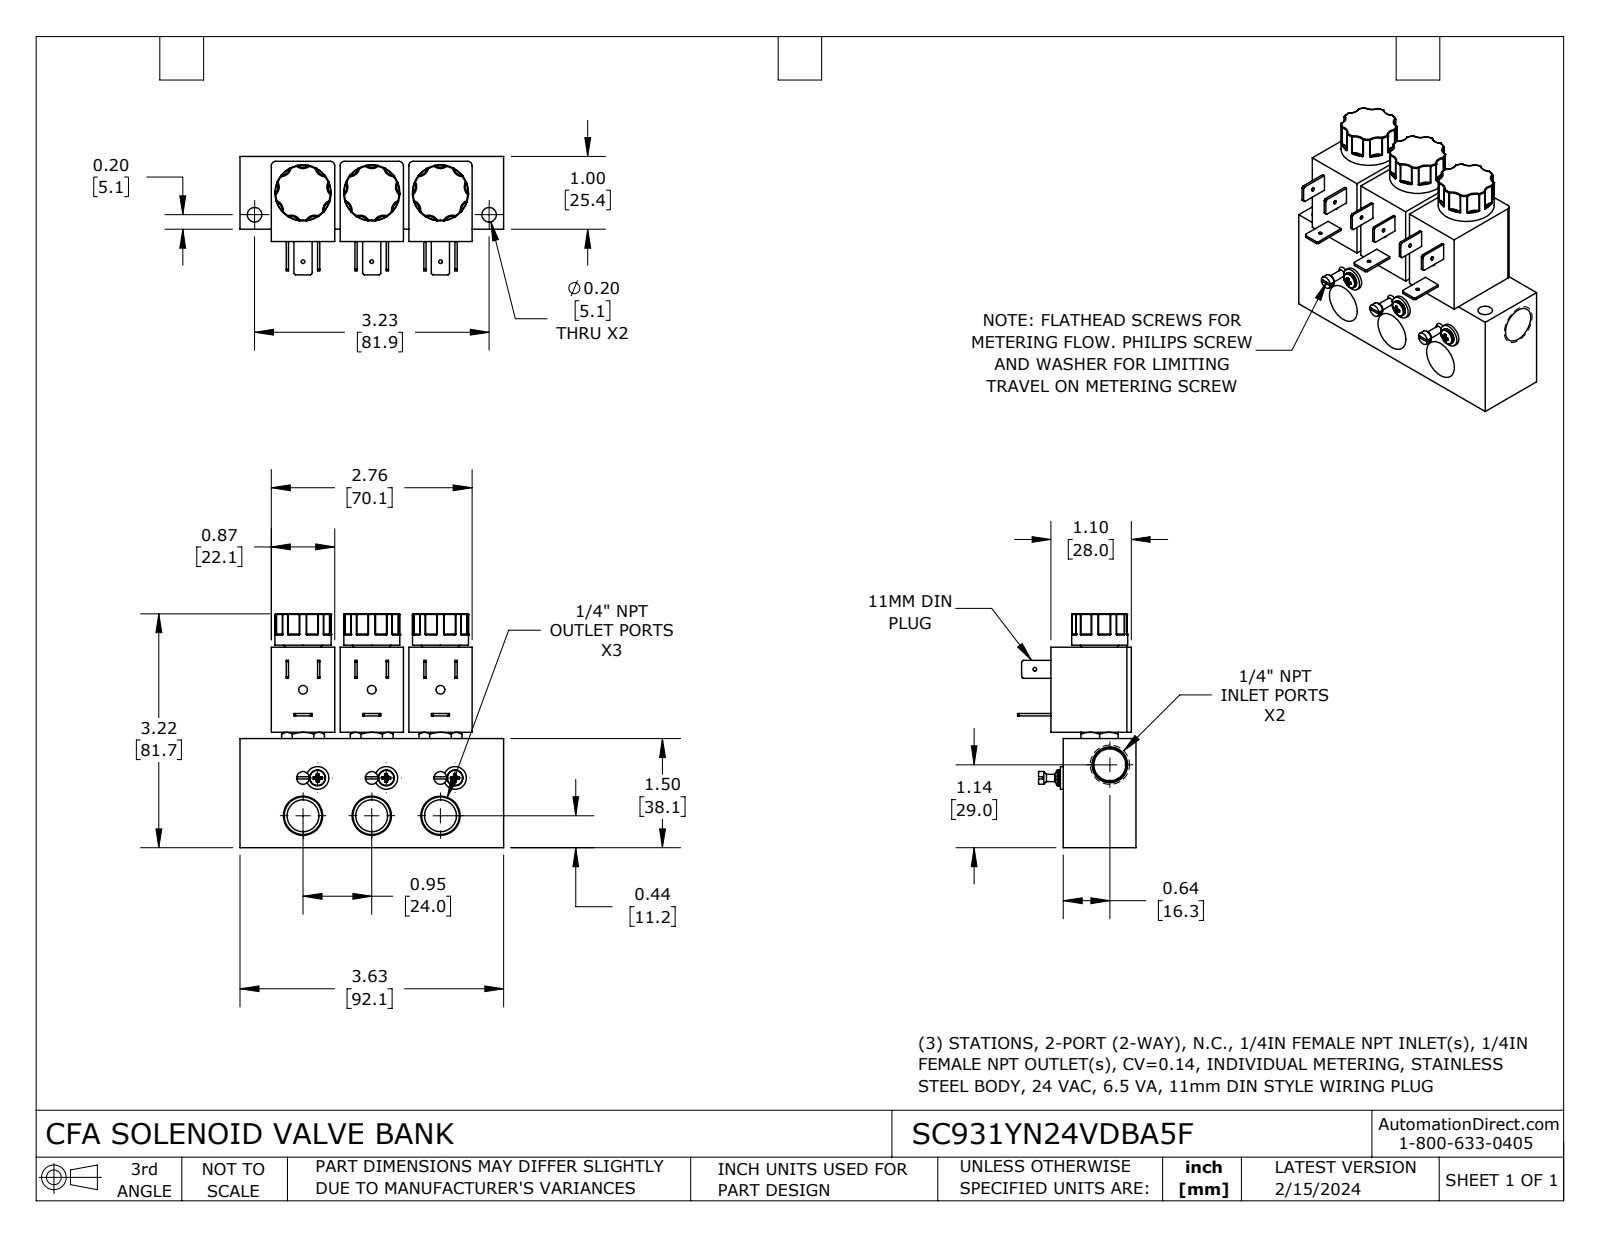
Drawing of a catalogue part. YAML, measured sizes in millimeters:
part_name: "SC931YN24VDBA5F"
step_written_by: "SolidWorks 2023 (CONFIG_CONTROL_DESIGN)"
units: millimeters
bodies: {solids: 1, faces: 829, planar: 215, cylindrical: 197, other: 417}
overall_size: [92.1, 81.7, 41.3]
volume: 144800
surface_area: 34630
round_holes:
  - {diameter: 1.3, count: 4}
  - {diameter: 11.1, count: 4}
  - {diameter: 3, count: 3}
  - {diameter: 5.1, count: 2}
round_bosses_or_shafts:
  - {diameter: 19.6, count: 3}
  - {diameter: 7.9, count: 3}
  - {diameter: 5.6, count: 3}
  - {diameter: 4.4, count: 3}
  - {diameter: 2.5, count: 3}
partial_cylinders:
  - {radius: 0.3, count: 54}
  - {radius: 3.4, count: 27}
  - {radius: 1.5, count: 6}
face_to_face_distances: [25.4, 24, 29.7, 4.3, 38.1, 24, 48, 1.7, 23.7, 28]
hole_center_spacings: [24, 24, 44, 48, 50.1, 50.1, 65.1, 23.6]
